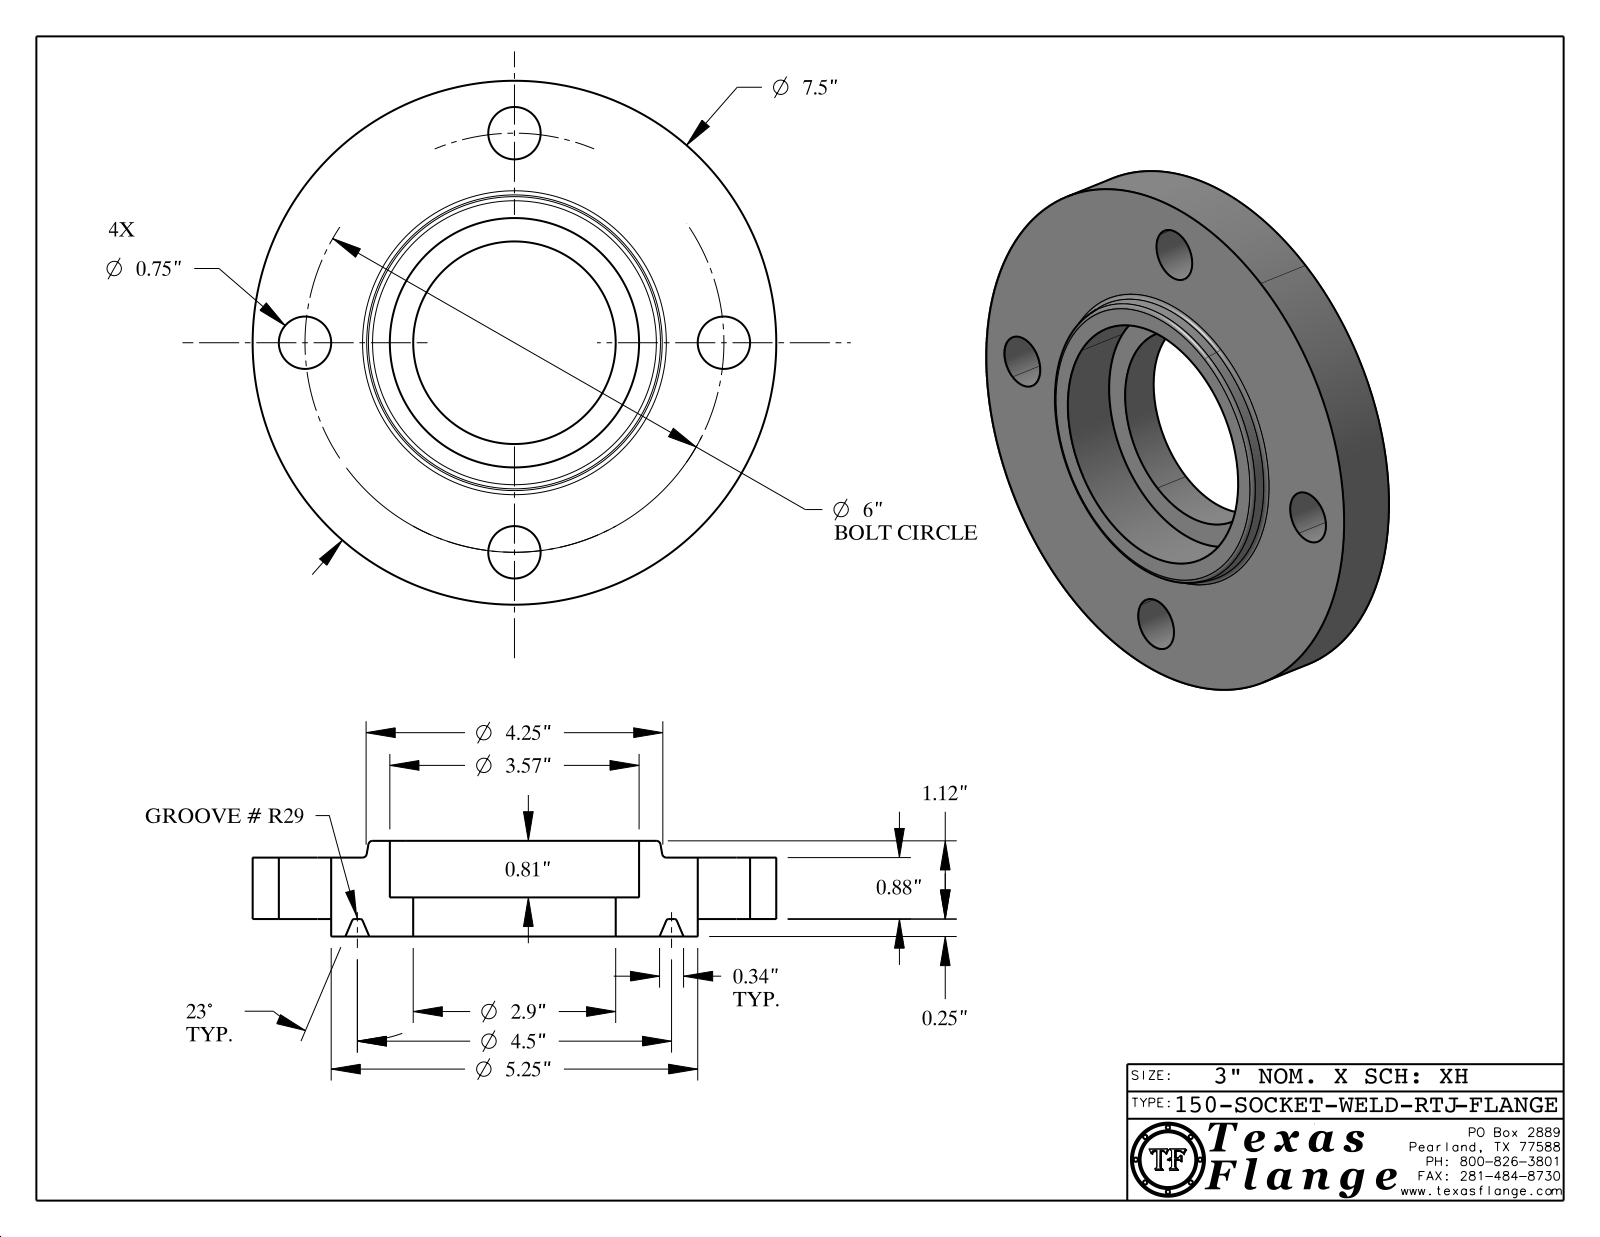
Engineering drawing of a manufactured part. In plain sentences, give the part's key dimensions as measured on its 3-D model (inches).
The part is named "150-SOCKET-WELD-RTJ". Its 3-D file was written by "CATIA V5 STEP AP214 (AUTOMOTIVE_DESIGN)". It is 1 solid with 422 faces: 372 planar, 36 cylindrical and 14 other. Overall it measures 7.5 by 7.5 by 1.37 inches. Its volume is 33.43 cubic inches and its surface area 125.8 square inches. Round holes: 4 of diameter 0.75, 1 of diameter 0.495, 1 of diameter 2.9, 1 of diameter 3.57. Round bosses or shafts: 8 of diameter 0.03, 1 of diameter 7.5, 1 of diameter 5.25, 1 of diameter 0.39. The main face-to-face distances are 0.88, 0.25, 1.13, 0.56, 0.31, 0.57, 1.37, 1.12, 0.81, 0.24. The hole center spacings are 3, 4.243, 2.296, 5.543, 6.
